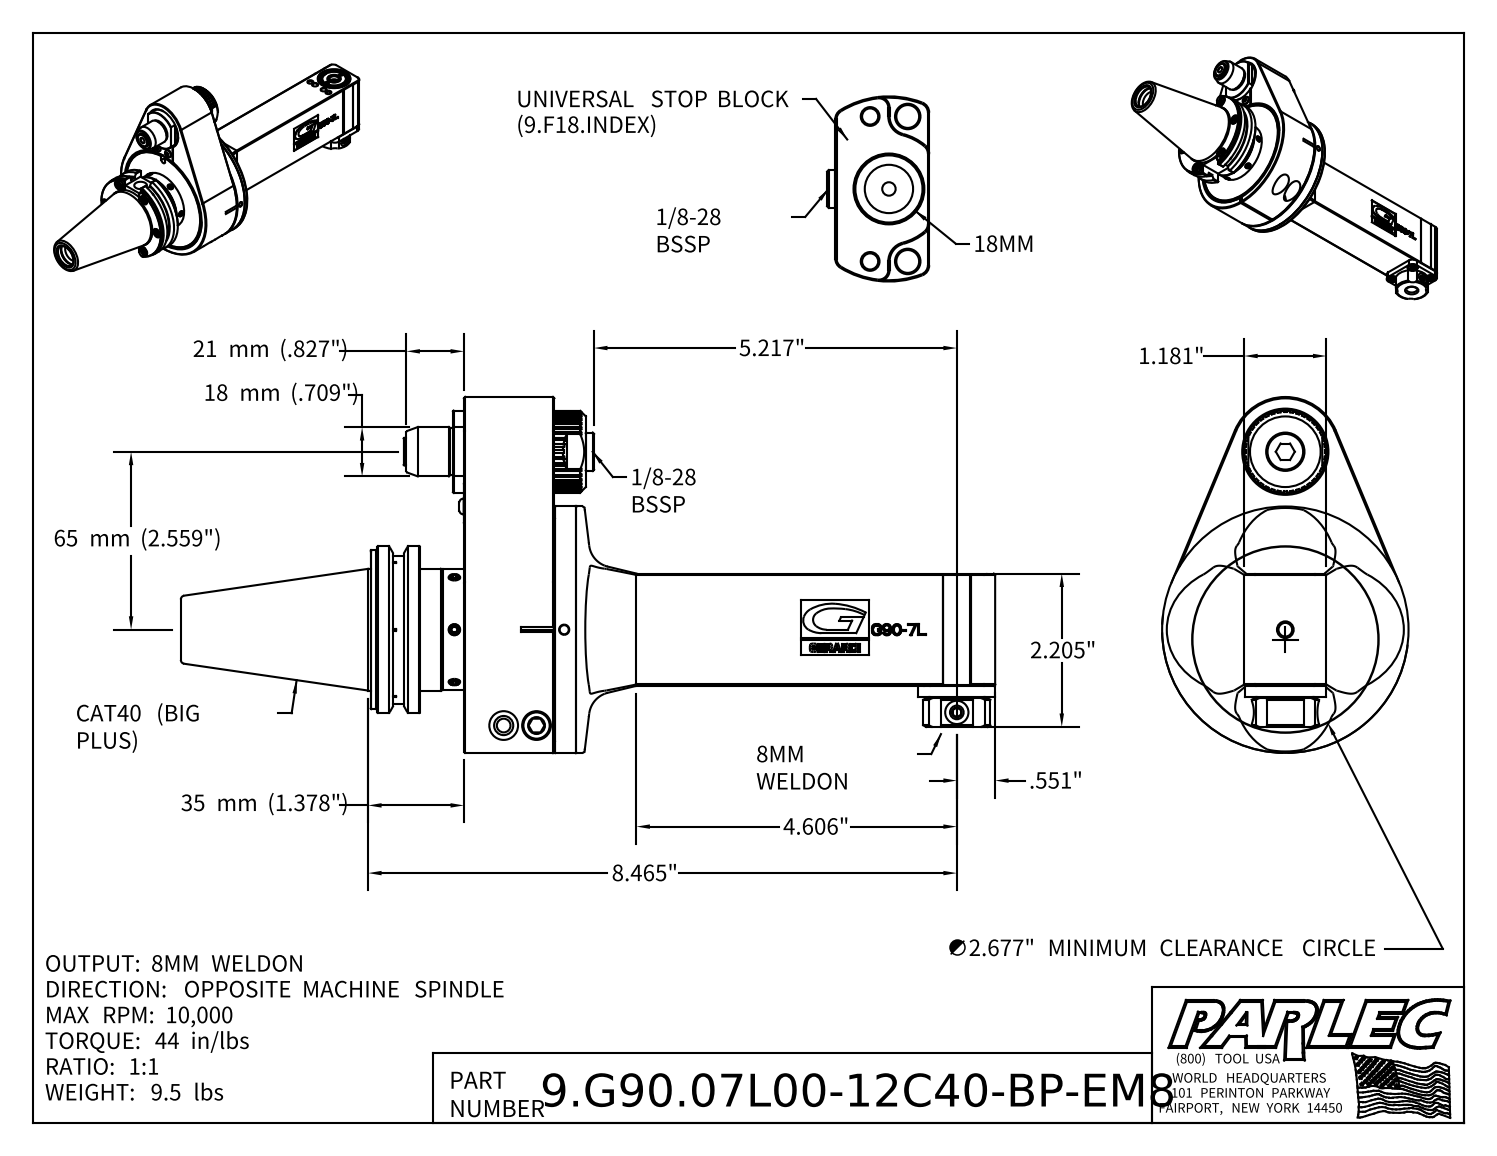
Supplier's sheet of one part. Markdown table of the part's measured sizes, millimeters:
| quantity | value |
| --- | --- |
| part name | 9.G90.07L00-12C40-BP-EM8 |
| STEP written by | Autodesk Inventor 2022 (AUTOMOTIVE_DESIGN) |
| units | millimeters |
| bodies | 3 solids, 1369 faces (788 planar, 251 cylindrical, 330 other) |
| overall size | 297.4 × 130 × 90 |
| volume | 593 120 mm³ |
| surface area | 137 757 mm² |
| round holes (diameter × count) | 3.3 × 10, 2.5 × 6, 4 × 4, 4.2 × 4, 5 × 4, 7.5 × 4, 7 × 3, 8.5 × 3, 2.1 × 2, 10.5 × 2, 5.5 × 1, 6.1 × 1 |
| round bosses / shafts (diameter × count) | 5.8 × 6, 3 × 6, 7 × 5, 10 × 4, 4 × 3, 30 × 2, 9 × 2, 5.7 × 2 |
| partial cylindrical surfaces (radius × count) | 3 × 9, 4 × 8, 4.25 × 4, 9 × 4, 1.5 × 3, 2 × 2, 2.15 × 2, 2.92 × 1 |
| main face-to-face distances | 30, 41, 3, 33, 8.5, 5.5, 24.5, 7, 1, 37 |
| hole center spacings | 27, 46.76, 11.1, 14.51, 19.9, 14, 54, 5 |
